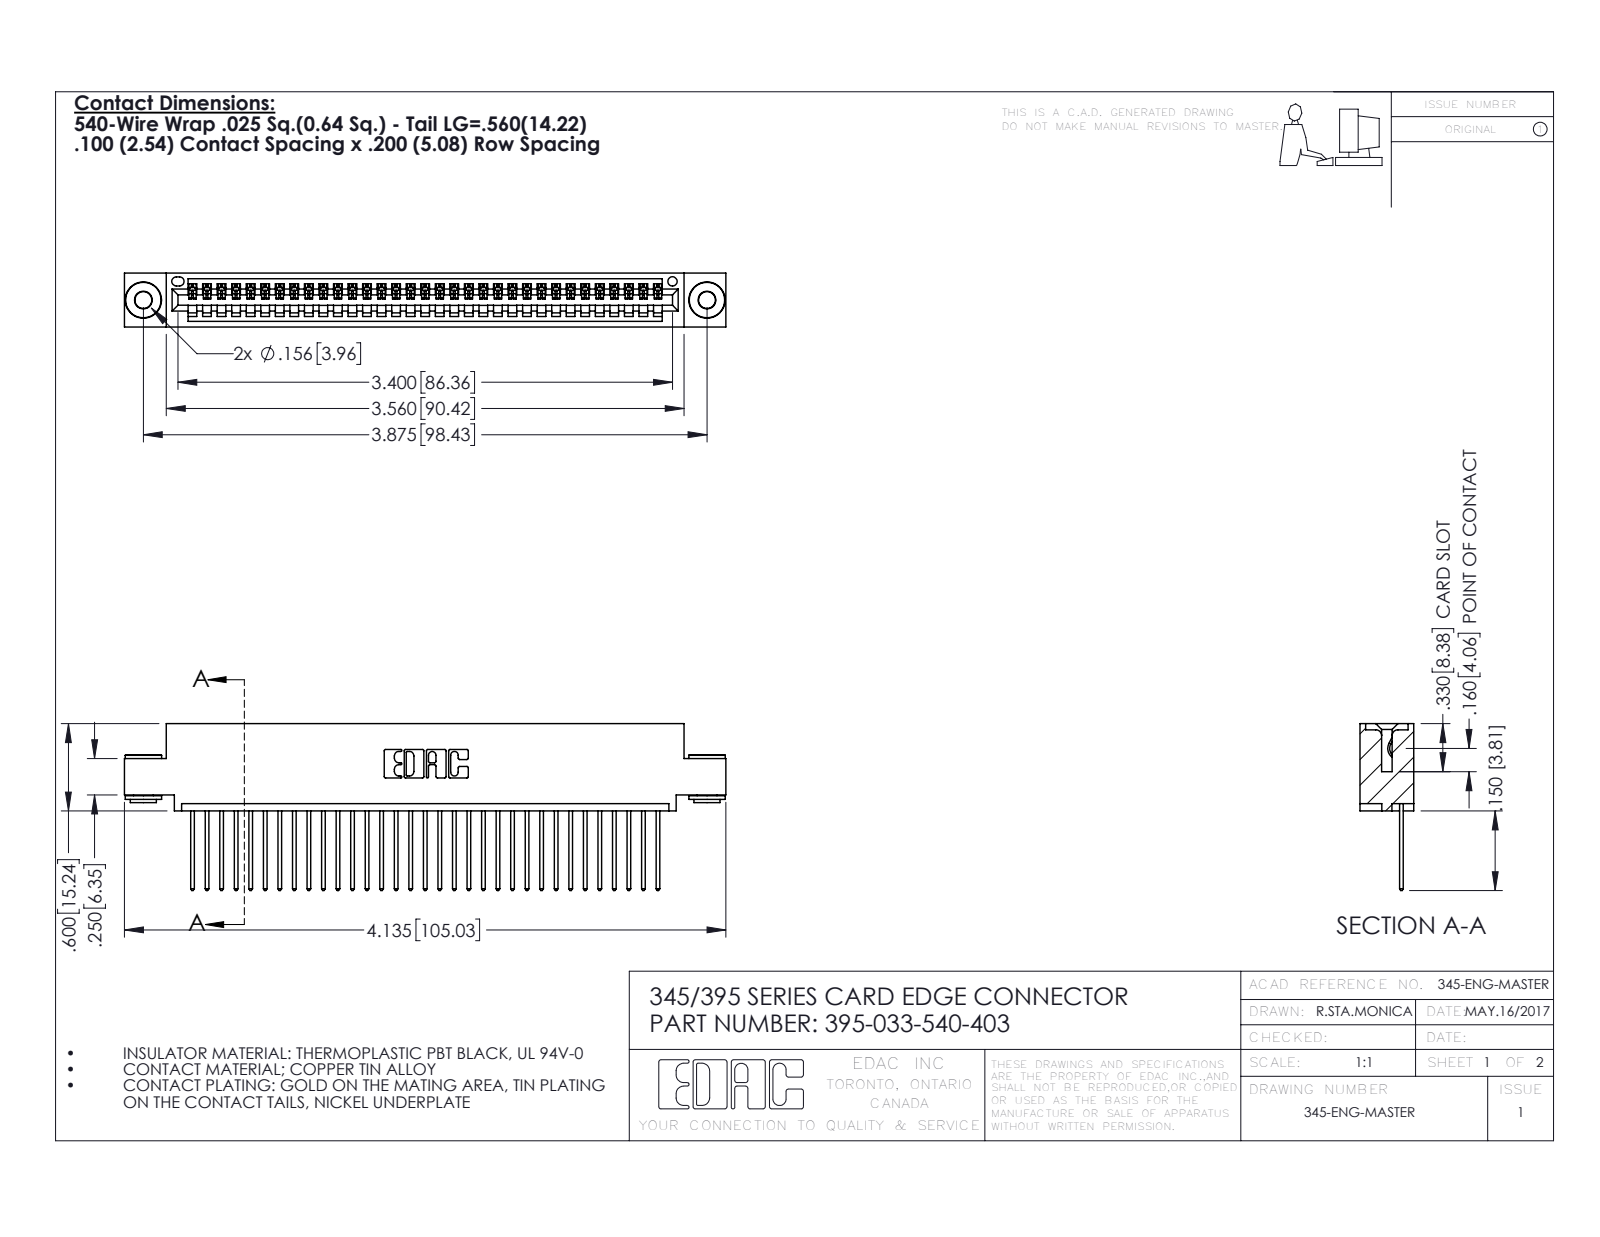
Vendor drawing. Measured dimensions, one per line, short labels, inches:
name: 345-250-002_345-250-002-102; 395-033-540-403; 345-292-001_345-293-140; 345 Part_0.110 Offset - 0.156 Dia-TH
written by: SolidWorks 2016 (CONFIG_CONTROL_DESIGN)
unit: in
bodies: 36 solids, 2082 faces (1414 planar, 660 cylindrical, 8 other)
size: 4.135 × 1.147 × 0.37
volume: 0.604 in³; area: 21.15 in²
holes: 2× ⌀0.116, 2× ⌀0.156, 1× ⌀0.064
bosses: 2× ⌀0.25, 2× ⌀0.18, 2× ⌀0.136
rounds: 66× R0.006, 66× R0.01, 22× R0.01, 6× R0.007, 6× R0.031, 3× R0.026, 2× R0.031, 2× R0.04
face distances: 0.072, 0.298, 0.37, 0.025, 0.2, 0.098, 0.272, 0.225, 0.149, 0.072
hole spacings: 0.27, 3.64, 3.875
